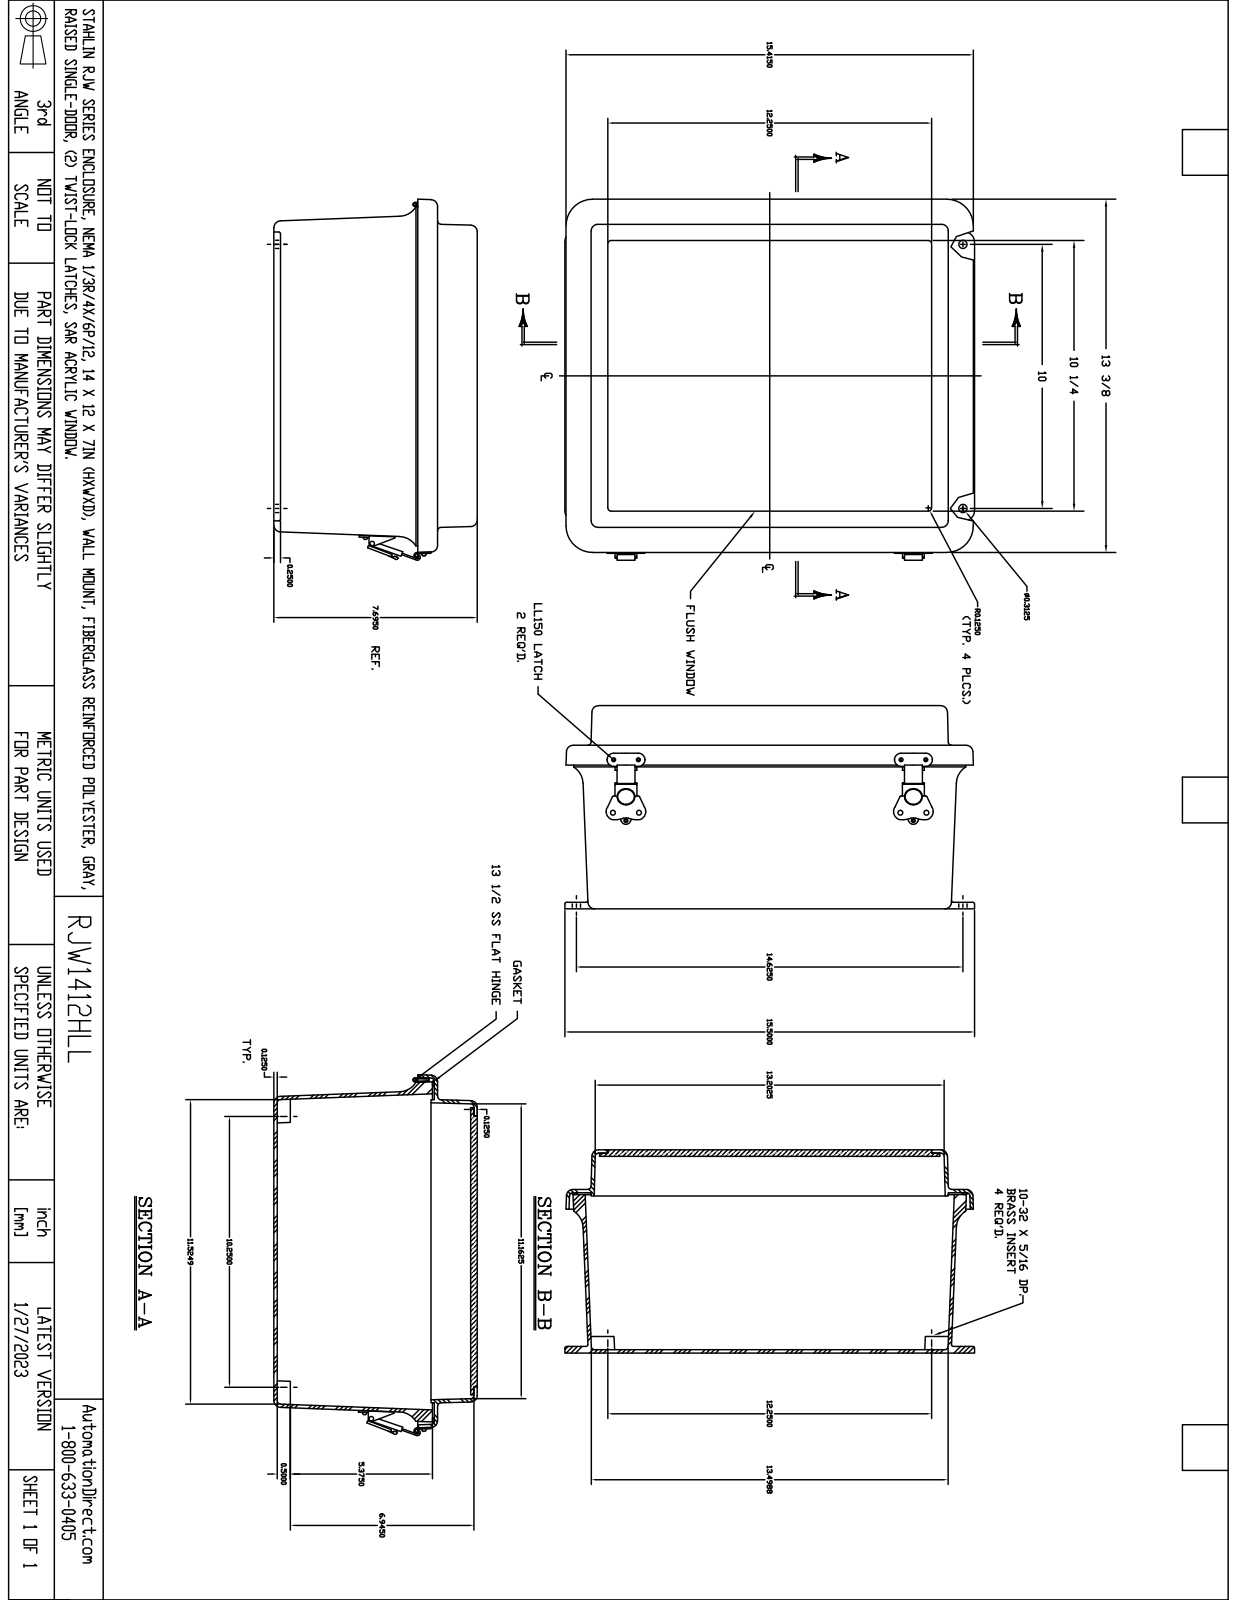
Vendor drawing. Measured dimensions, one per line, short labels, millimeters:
name: MRW1412HLL
written by: SolidWorks 2018 (AUTOMOTIVE_DESIGN)
unit: mm
bodies: 51 solids, 1302 faces (581 planar, 504 cylindrical, 217 other)
size: 393.7 × 344.9 × 195.7
volume: 2 243 000 mm³; area: 1 152 000 mm²
holes: 18× ⌀3.6, 10× ⌀3.3, 8× ⌀3.9, 4× ⌀3.3, 4× ⌀4, 4× ⌀4.2, 4× ⌀5, 4× ⌀5.5, 2× ⌀3, 2× ⌀3.5, 2× ⌀4.6, 2× ⌀4.6
bosses: 18× ⌀6.4, 9× ⌀3.2, 9× ⌀3.2, 4× ⌀6.9, 2× ⌀14.8, 2× ⌀13.3, 2× ⌀5.3, 2× ⌀4.7
rounds: 24× R3.2, 24× R6.4, 20× R0.8, 19× R2, 8× R0.9, 8× R1, 8× R1.1, 8× R1.2
face distances: 3.2, 189.3, 3.2, 6.4, 195.7, 192.5, 186.1, 151.2, 38.1, 41.3
hole spacings: 82.6, 165.1, 276.4, 247.7, 6.4, 76.2, 23.8, 34.8
